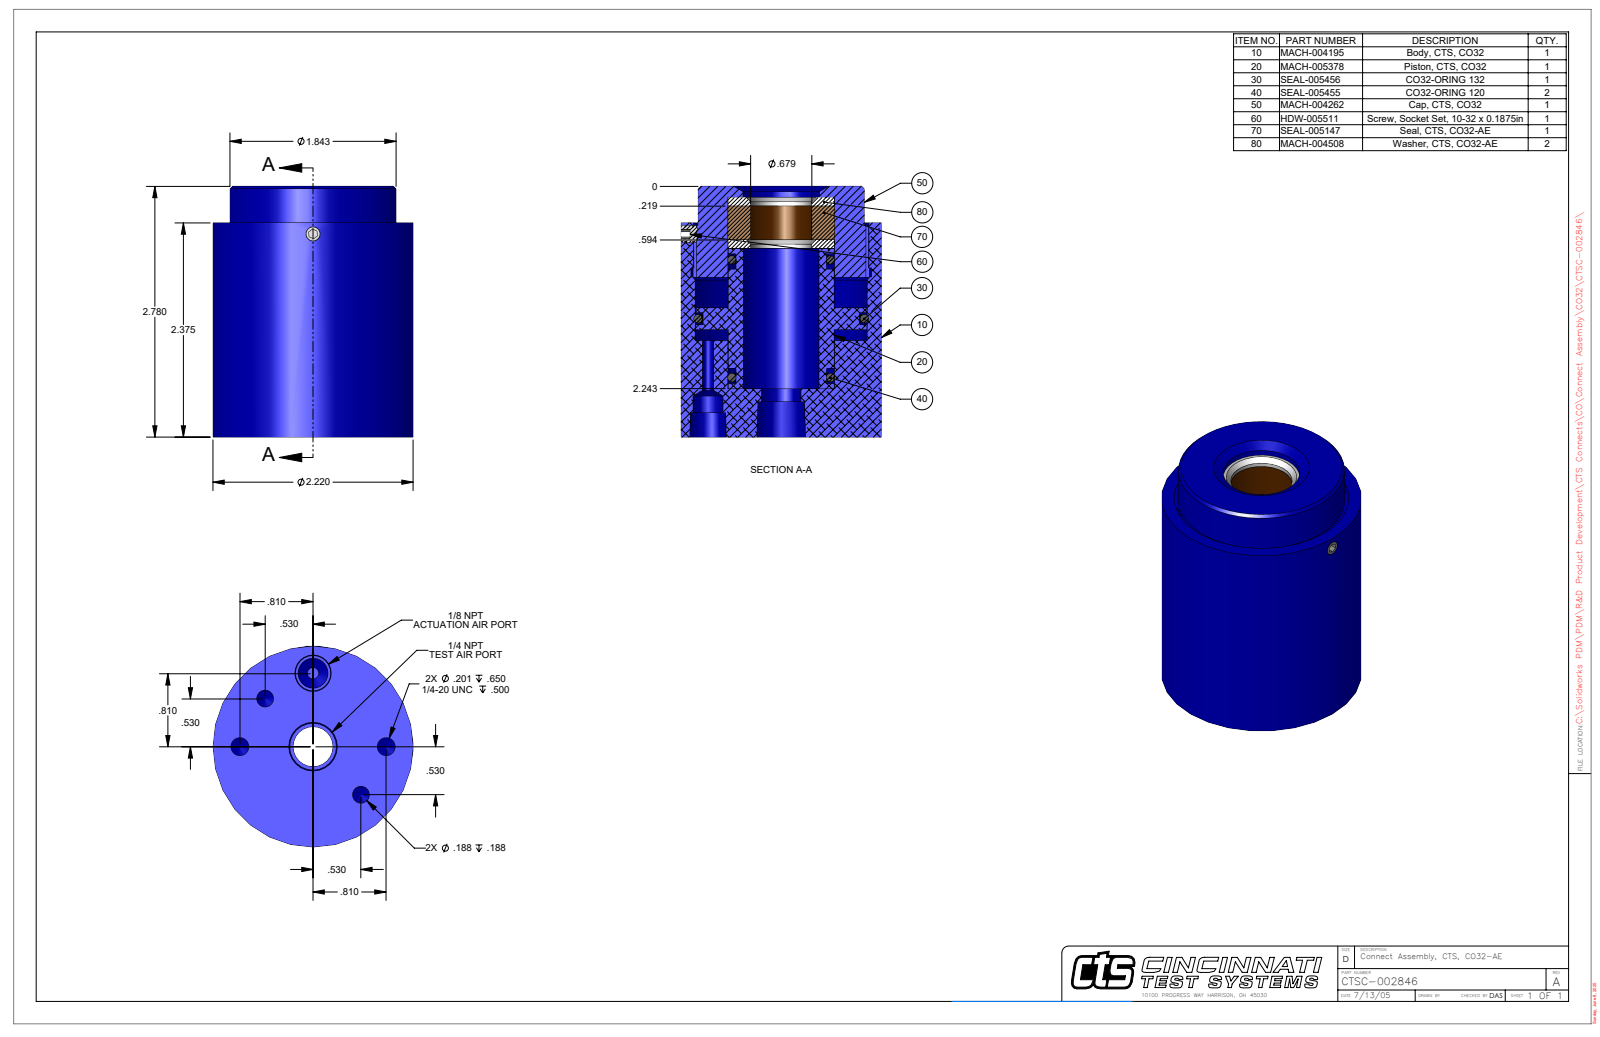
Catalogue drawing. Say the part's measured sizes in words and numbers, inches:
The part is named "CTSC-002846". Its 3-D file was written by "SolidWorks 2023 (AUTOMOTIVE_DESIGN)". It is 1 solid with 124 faces: 51 planar, 48 cylindrical and 25 other. Overall it measures 2.78 by 2.22 by 2.22 inches. Its volume is 8.903 cubic inches and its surface area 35.57 square inches. Round holes: 2 of diameter 0.187, 2 of diameter 0.201, 1 of diameter 0.094, 1 of diameter 0.125, 1 of diameter 0.159, 1 of diameter 0.332, 1 of diameter 0.438, 1 of diameter 0.679, 1 of diameter 0.681, 1 of diameter 0.837, 1 of diameter 0.848, 1 of diameter 0.861. Round bosses or shafts: 1 of diameter 2.22, 1 of diameter 1.843, 1 of diameter 1.172. Partial cylindrical surfaces (rounded edges, fillets, slot ends): 1 of radius 0.095, 1 of radius 1.095. The main face-to-face distances are 2.78, 2.375, 0.405, 0.537, 1.837, 2.243, 2.343, 1.805, 0.032, 0.437. The hole center spacings are 0.6, 0.81, 1.441, 0.75, 1.145, 1.5, 1.62.
